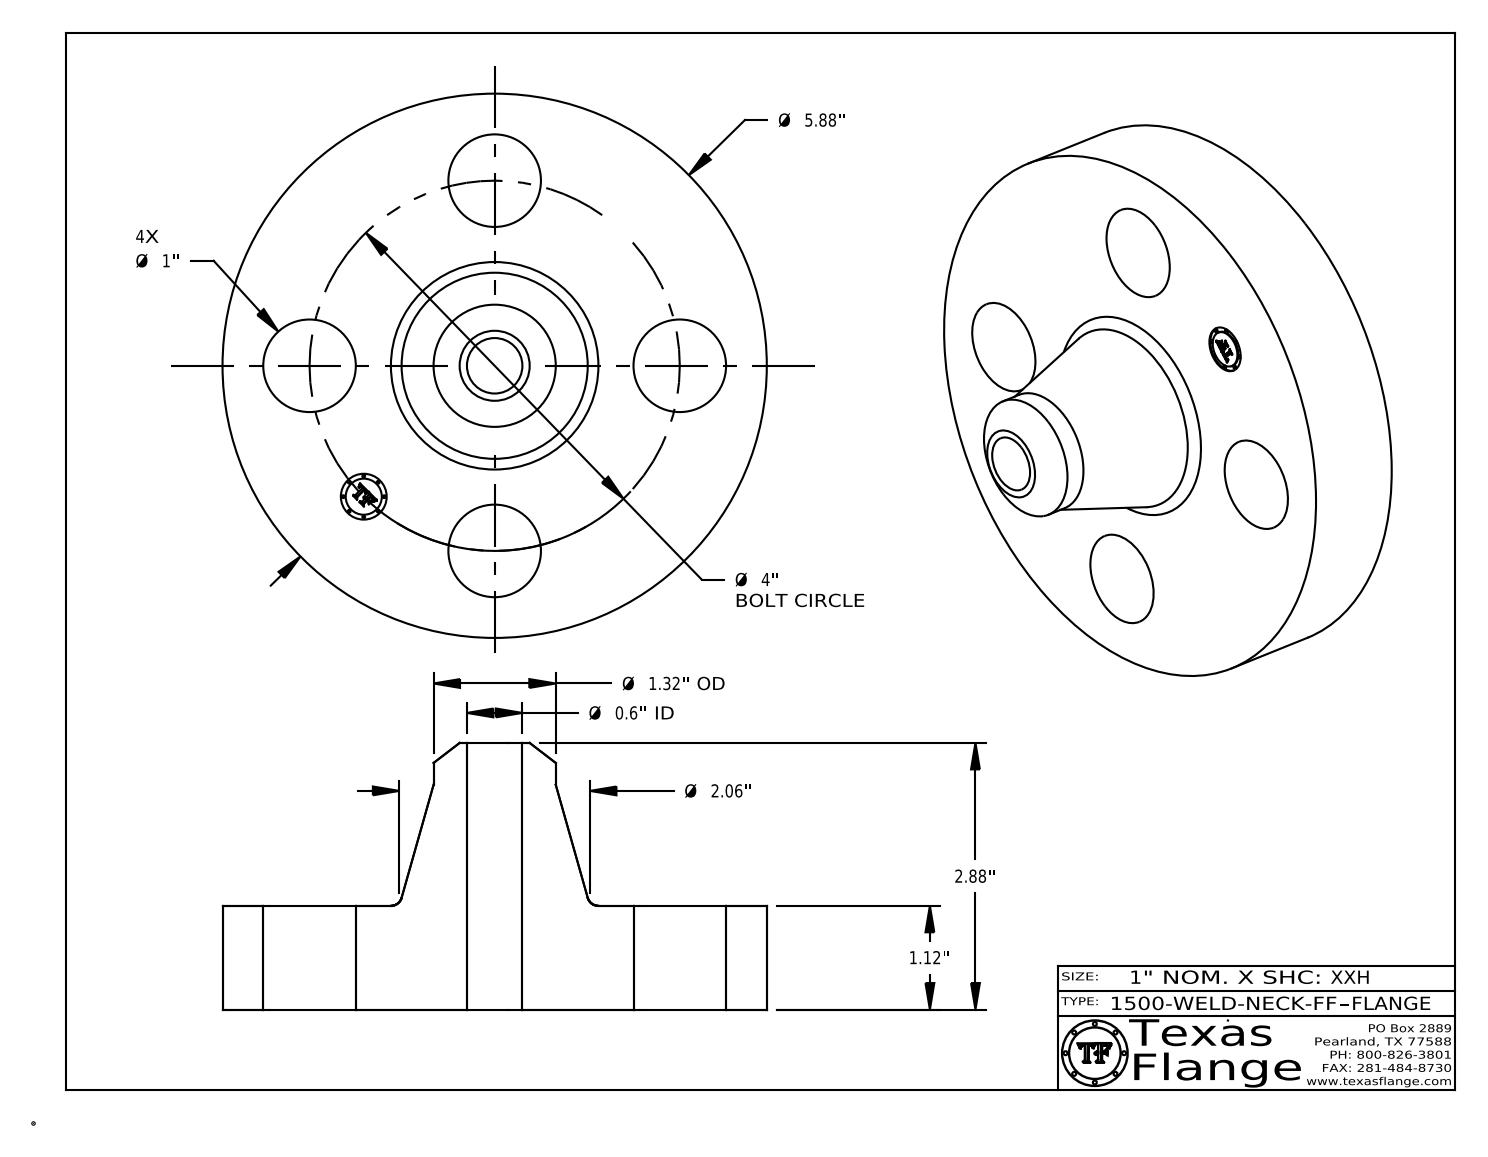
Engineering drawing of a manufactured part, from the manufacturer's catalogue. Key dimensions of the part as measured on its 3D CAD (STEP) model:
Part name (STEP PRODUCT): 1500-WELD-NECK-FF
STEP written by: CATIA V5 STEP AP214 (AUTOMOTIVE_DESIGN)
Units: inches
Bodies: 1 solid, 408 faces (368 planar, 34 cylindrical, 6 other)
Overall size (bounding box): 5.88 × 5.88 × 2.88
Volume: 29.58 in³ · Surface area: 94.04 in²
Round holes (diameter × count): ⌀1 ×4, ⌀0.495 ×1, ⌀0.599 ×1
Round bosses / shafts (diameter × count): ⌀0.03 ×8, ⌀5.88 ×1, ⌀1.32 ×1, ⌀0.39 ×1
Main face-to-face distances: 1.12, 2.88, 1.76, 0.015, 1.105, 1.775, 0.148, 0.145, 0.027, 0.096
Hole centre spacings: 2, 2.828, 1.531, 3.695, 4
